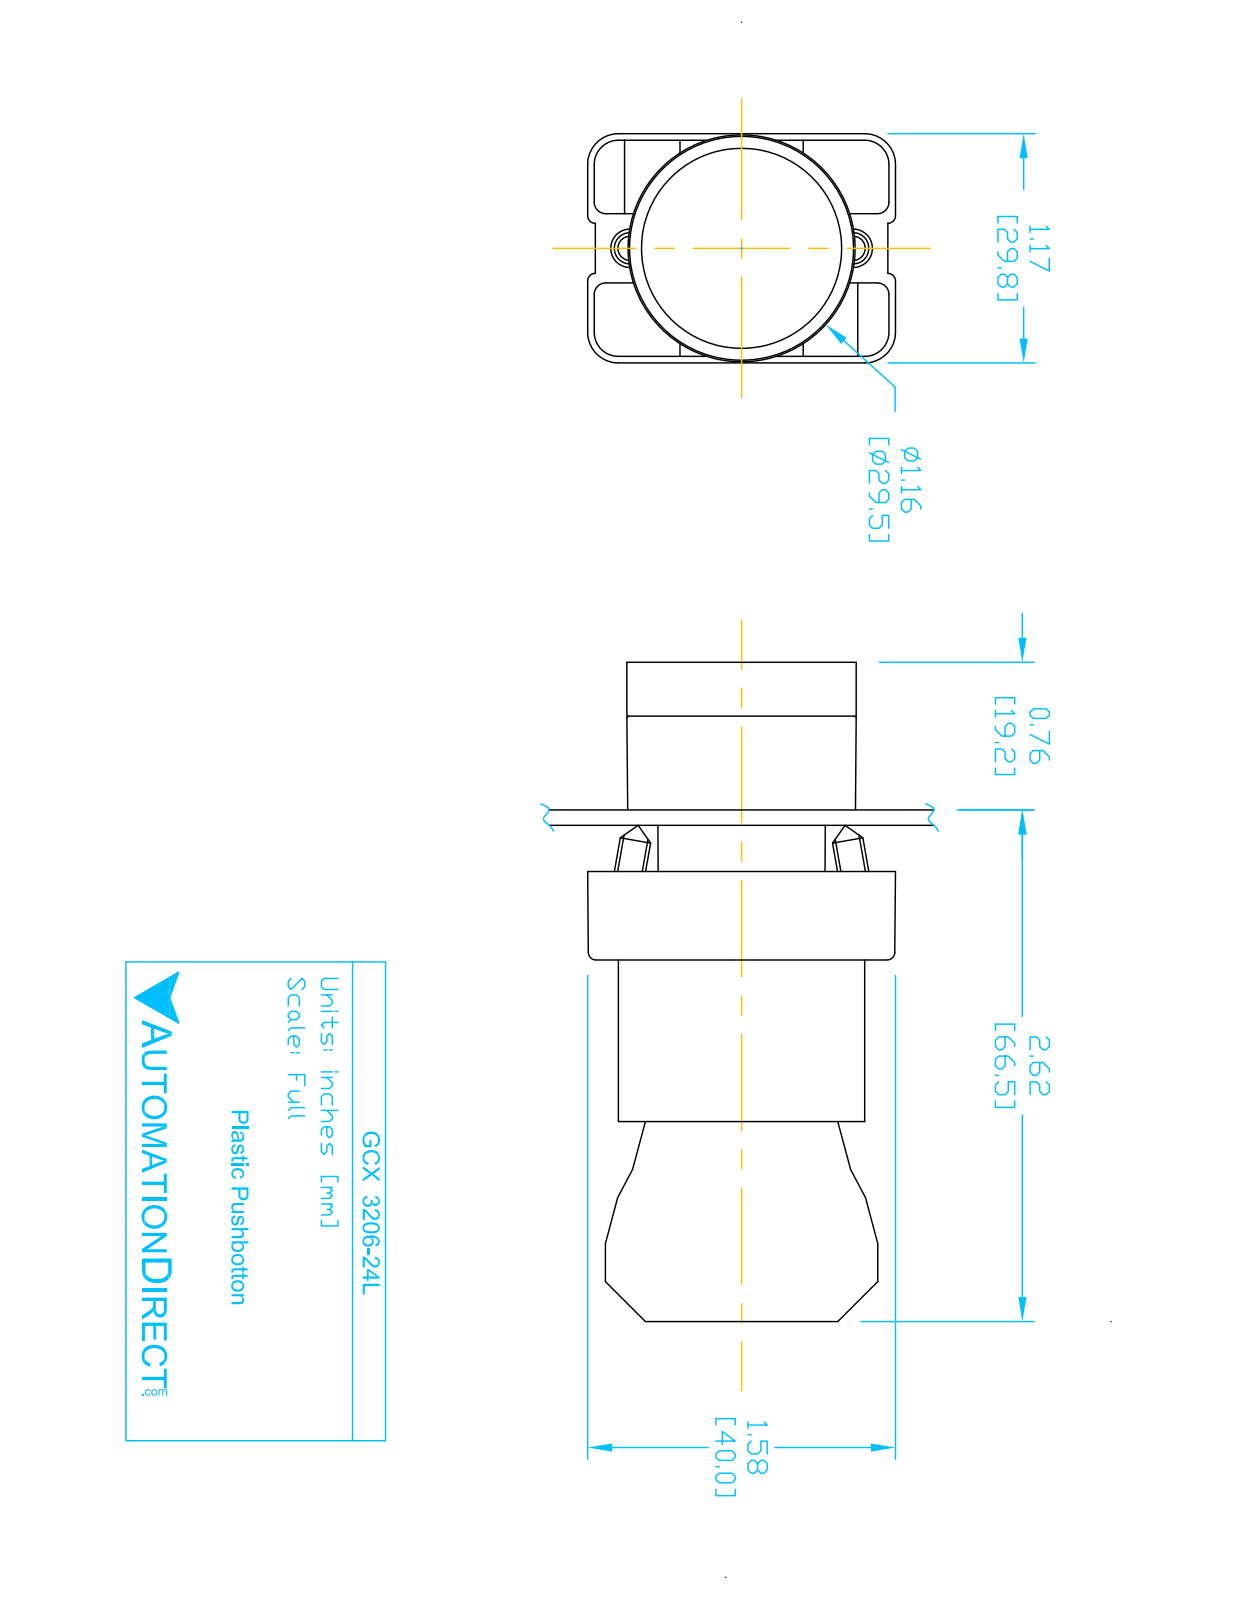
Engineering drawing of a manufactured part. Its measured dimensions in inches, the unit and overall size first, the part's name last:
Units: inches
Overall size (bounding box): 3.319 × 1.581 × 1.177
Round holes (diameter × count): ⌀0.079 ×2, ⌀0.124 ×2, ⌀0.13 ×2, ⌀0.087 ×1, ⌀0.197 ×1, ⌀0.469 ×1, ⌀0.878 ×1, ⌀0.888 ×1, ⌀1.024 ×1
Round bosses / shafts (diameter × count): ⌀0.157 ×4, ⌀1.175 ×1, ⌀1.004 ×1, ⌀0.945 ×1, ⌀0.856 ×1, ⌀0.78 ×1, ⌀0.504 ×1
Partial cylindrical surfaces — rounded edges, fillets, slot ends (radius × count): R0.059 ×24, R0.041 ×12, R0.124 ×12, R0.157 ×12, R0.039 ×8, R0.128 ×2, R0.02 ×1, R0.063 ×1
Main face-to-face distances: 0.827, 0.579, 2.02, 1.193, 1.171, 0.276, 2.295, 1.469, 0.031, 0.033
Hole centre spacings: 0.236, 0.544, 0.472, 0.49
Volume: 2.794 in³ · Surface area: 38.77 in²
Bodies: 8 solids, 431 faces (252 planar, 148 cylindrical, 31 other)
Part name (STEP PRODUCT): ECX3029-2; ECX1050; GCX3206-24L; GCX3206L OPERATOR (+1 more)
STEP written by: SolidWorks 2016 (AUTOMOTIVE_DESIGN)
